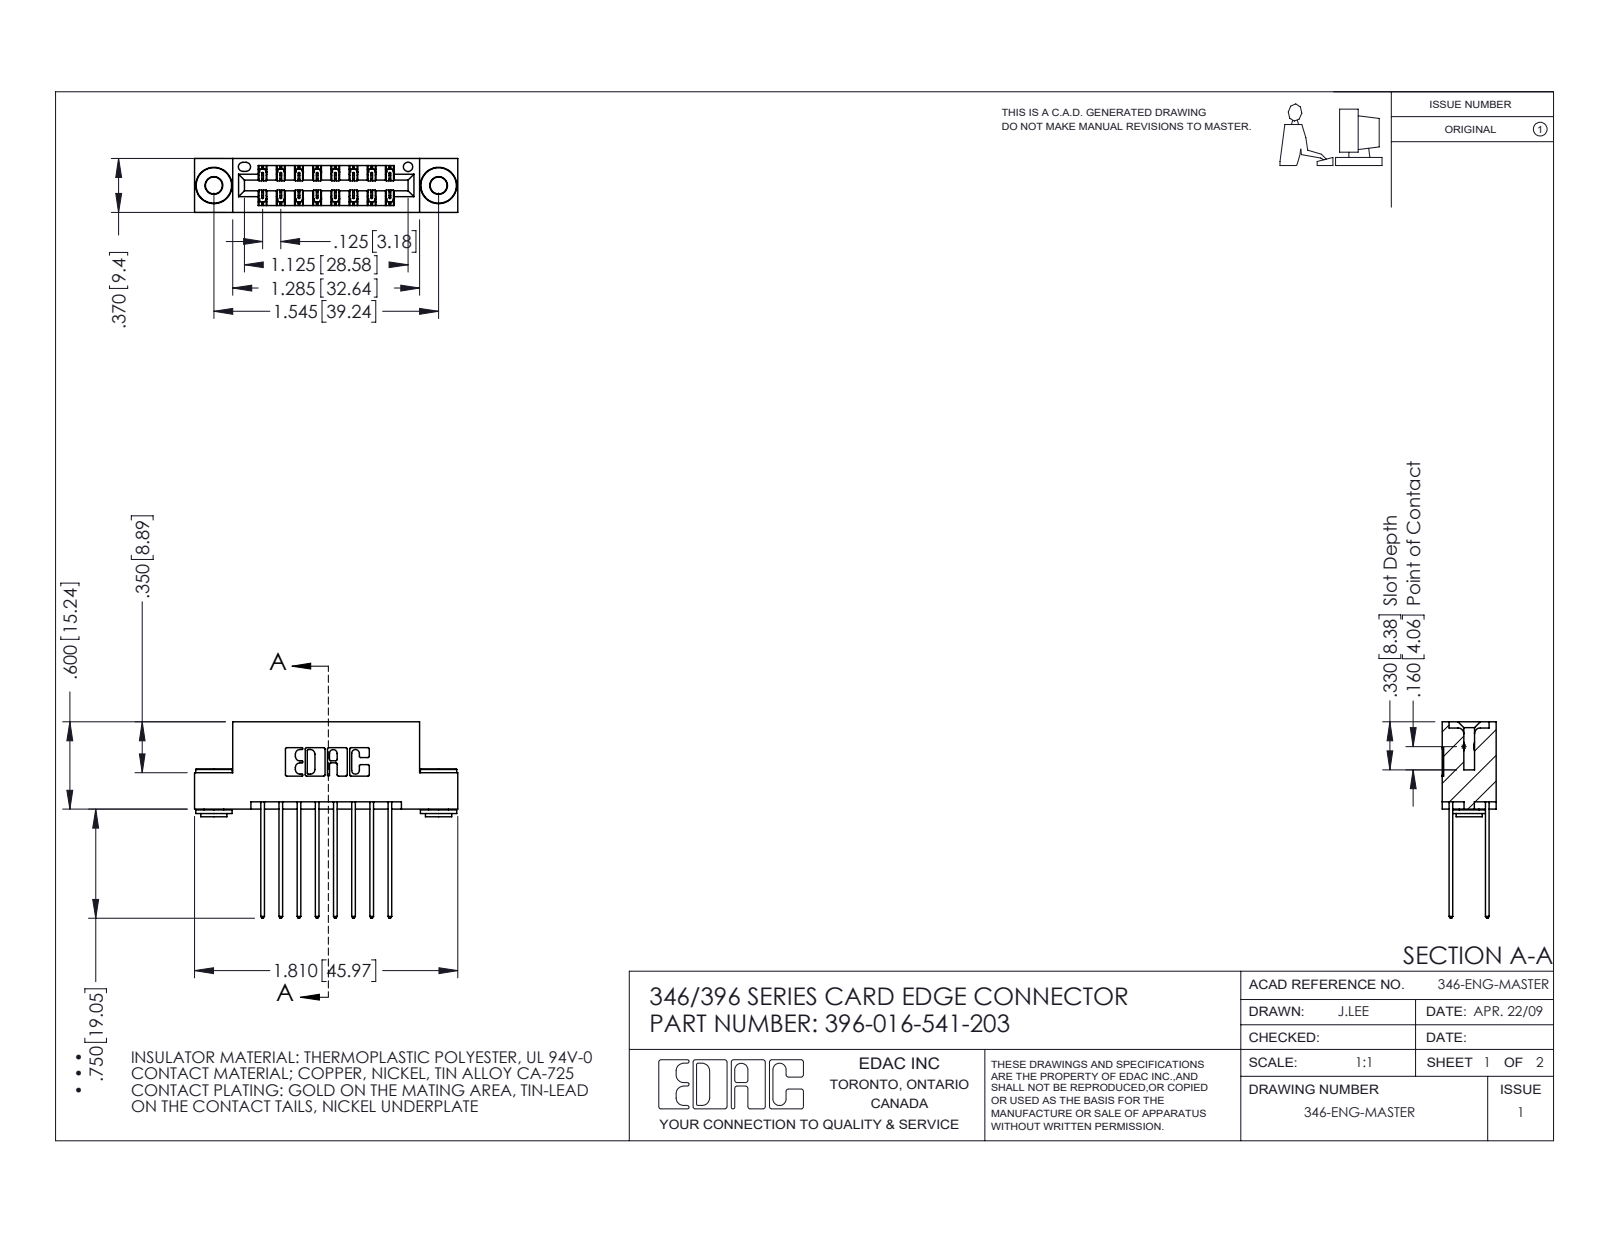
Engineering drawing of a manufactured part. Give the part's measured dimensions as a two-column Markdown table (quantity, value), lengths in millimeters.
| quantity | value |
| --- | --- |
| part name | 345-292-001_345-293-141; 346 Part_Flush Mounting Lugs - 0.156 Dia-TH; 345-250-002_345-250-002-102; 396-016-541-203 |
| STEP written by | SolidWorks 2016 (CONFIG_CONTROL_DESIGN) |
| units | millimeters |
| bodies | 19 solids, 992 faces (646 planar, 338 cylindrical, 8 other) |
| overall size | 46 × 34.3 × 9.4 |
| volume | 4 330 mm³ |
| surface area | 6 072 mm² |
| round holes (diameter × count) | 2.9 × 2, 4 × 2, 1.6 × 1 |
| round bosses / shafts (diameter × count) | 6.4 × 2, 4.6 × 2, 3.5 × 2 |
| partial cylindrical surfaces (radius × count) | 0.2 × 24, 0.3 × 22, 0.3 × 16, 0.2 × 6, 0.8 × 6, 0.7 × 3, 0.4 × 2, 0.6 × 2 |
| main face-to-face distances | 6.4, 1.2, 8.2, 9.4, 0.6, 1.8, 7.6, 7, 12.7, 5.7 |
| hole center spacings | 6.2, 34.1, 39.2 |
